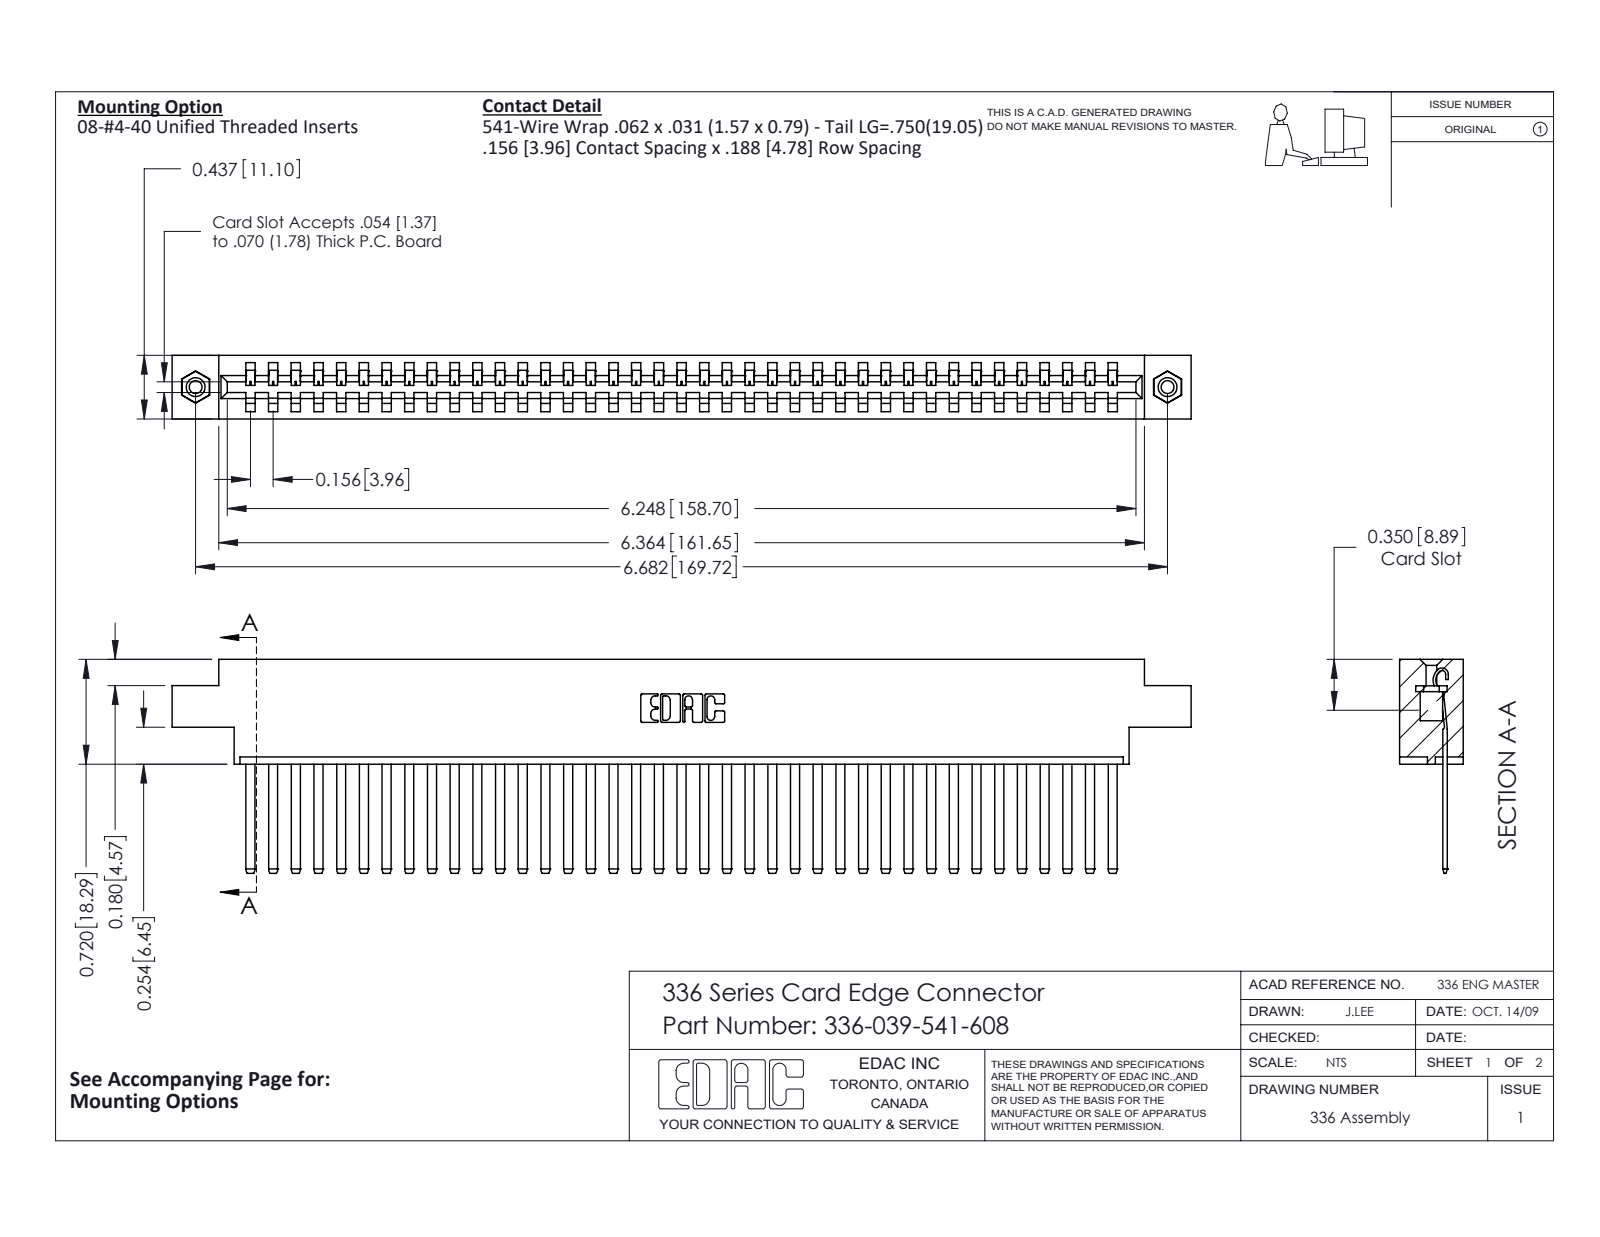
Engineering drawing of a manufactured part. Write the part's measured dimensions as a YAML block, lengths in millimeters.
part_name: "345-250-001_345-250-003-102; 336-039-541-608; 336-290-001_336-290-541; 336 Part_Offset - .156 Dia - TI"
step_written_by: "SolidWorks 2020 (CONFIG_CONTROL_DESIGN)"
units: millimeters
bodies: {solids: 42, faces: 2128, planar: 1432, cylindrical: 680, other: 16}
overall_size: [177.9, 37.3, 11.1]
volume: 25830
surface_area: 28190
round_holes:
  - {diameter: 2.3, count: 2}
  - {diameter: 3.2, count: 2}
  - {diameter: 4, count: 2}
round_bosses_or_shafts:
  - {diameter: 3.9, count: 2}
partial_cylinders:
  - {radius: 0.1, count: 78}
  - {radius: 1.4, count: 78}
  - {radius: 0.3, count: 22}
  - {radius: 0.2, count: 6}
  - {radius: 0.8, count: 6}
  - {radius: 0.7, count: 3}
  - {radius: 0.6, count: 2}
  - {radius: 1, count: 2}
face_to_face_distances: [11.1, 4.6, 8.3, 3.6, 7.5, 2.8, 0.8, 6.5, 1.3, 3.3]
hole_center_spacings: [169.7]
